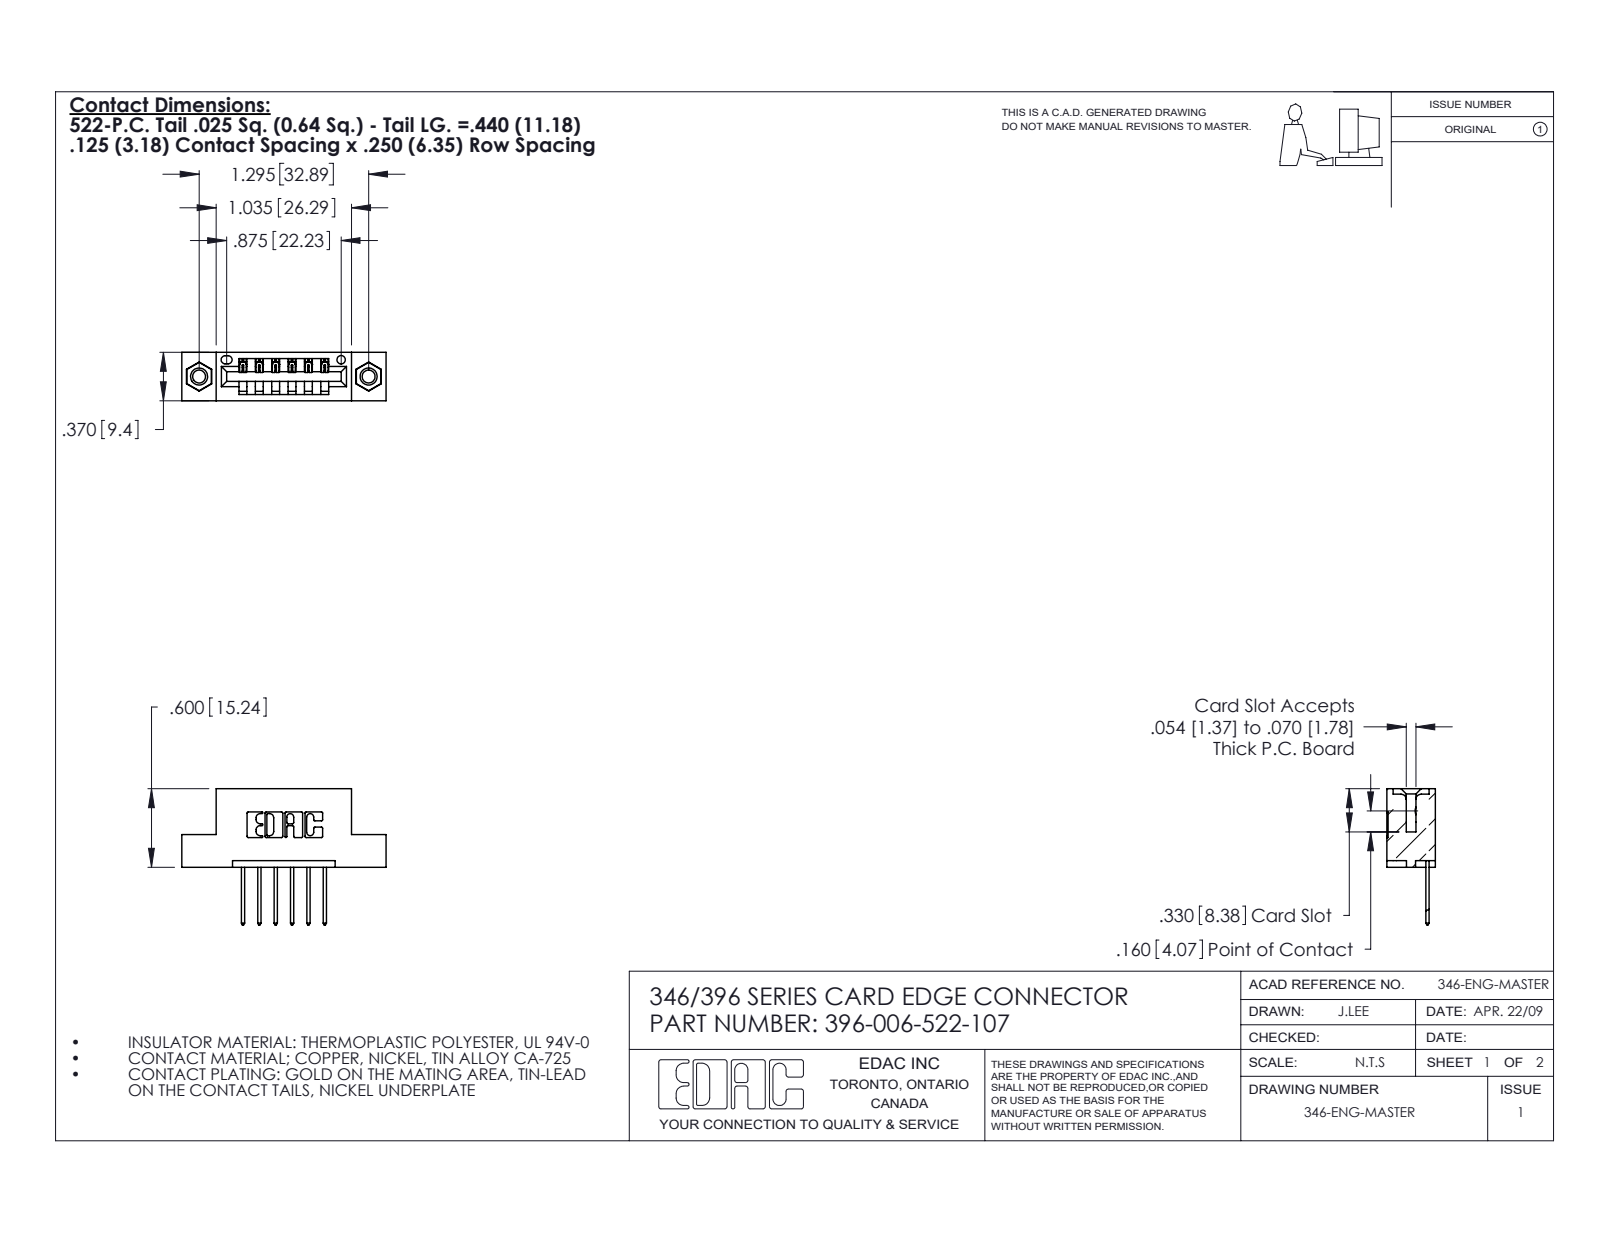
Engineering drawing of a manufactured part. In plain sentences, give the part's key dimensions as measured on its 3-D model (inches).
The part is named "345-292-001_345-293-122; 396-006-522-107; 345-250-001_345-250-005-103; 346 Part_Flush Mounting Lugs - 0.156 Dia-TI". Its 3-D file was written by "SolidWorks 2020 (CONFIG_CONTROL_DESIGN)". It is 9 solids with 530 faces: 348 planar, 166 cylindrical and 16 other. Overall it measures 1.56 by 1.04 by 0.37 inches. Its volume is 0.216 cubic inches and its surface area 6.329 square inches. Round holes: 2 of diameter 0.098, 2 of diameter 0.125, 2 of diameter 0.156, 1 of diameter 0.064. Round bosses or shafts: 2 of diameter 0.155. Partial cylindrical surfaces (rounded edges, fillets, slot ends): 22 of radius 0.01, 12 of radius 0.006, 12 of radius 0.01, 6 of radius 0.007, 6 of radius 0.031, 3 of radius 0.026, 2 of radius 0.031, 2 of radius 0.04. The main face-to-face distances are 0.25, 0.37, 0.048, 0.322, 0.072, 0.298, 0.025, 0.148, 0.222, 0.1. The hole center spacings are 0.246, 1.092, 1.295.
